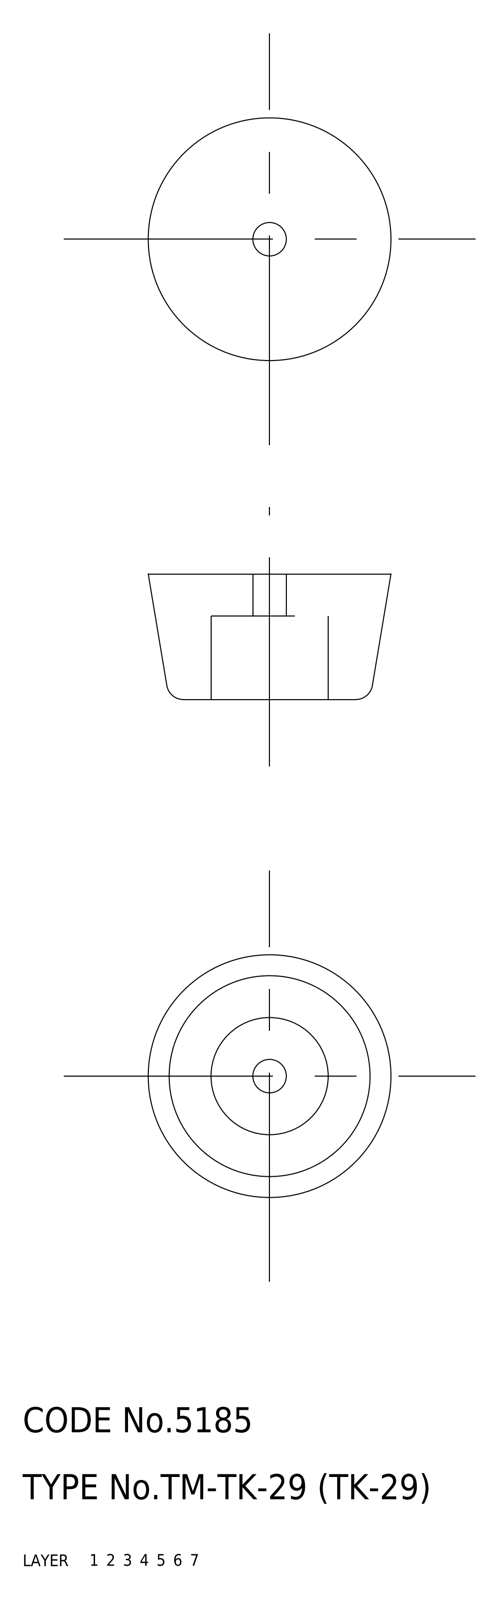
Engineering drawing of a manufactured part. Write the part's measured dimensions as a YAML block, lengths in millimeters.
part_name: "washer; rubber foot; TK_29_9594_36"
step_written_by: "CADfix (AUTOMOTIVE_DESIGN)"
units: millimeters
bodies: {solids: 2, faces: 20, planar: 0, cylindrical: 0, other: 20}
overall_size: [29, 29, 15]
volume: 6670
surface_area: 3365
